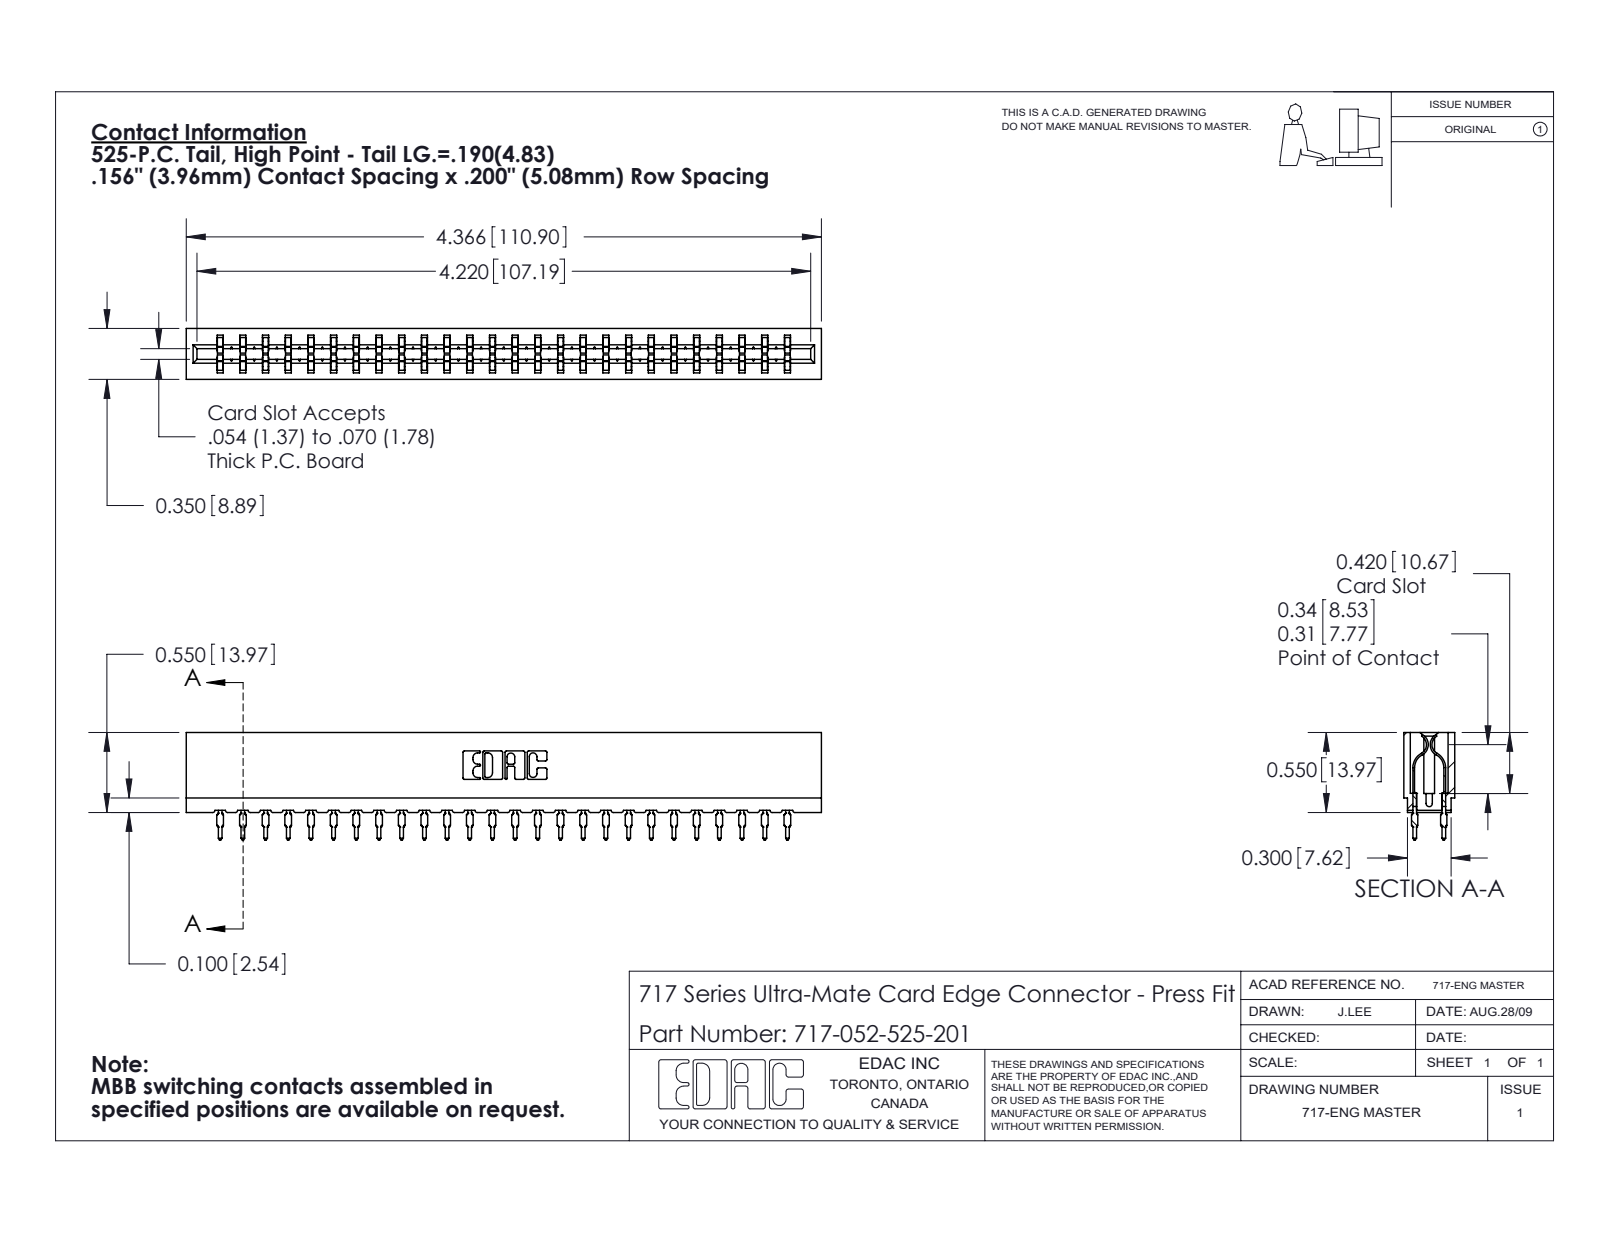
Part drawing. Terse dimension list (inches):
name: 717-052-525-201; 745-292-001_525; 717 Part_Insulator Option - 06
written by: SolidWorks 2020 (CONFIG_CONTROL_DESIGN)
unit: in
bodies: 53 solids, 4774 faces (2472 planar, 950 cylindrical, 1352 other)
size: 4.366 × 0.739 × 0.35
volume: 0.59 in³; area: 22.49 in²
rounds: 104× R0.021, 52× R0.015, 22× R0.01, 8× R0.005, 8× R0.011, 6× R0.007, 6× R0.031, 3× R0.026
face distances: 0.212, 0.138, 0.35, 0.063, 0.287, 0.076, 0.149, 0.156, 0.074, 0.045
